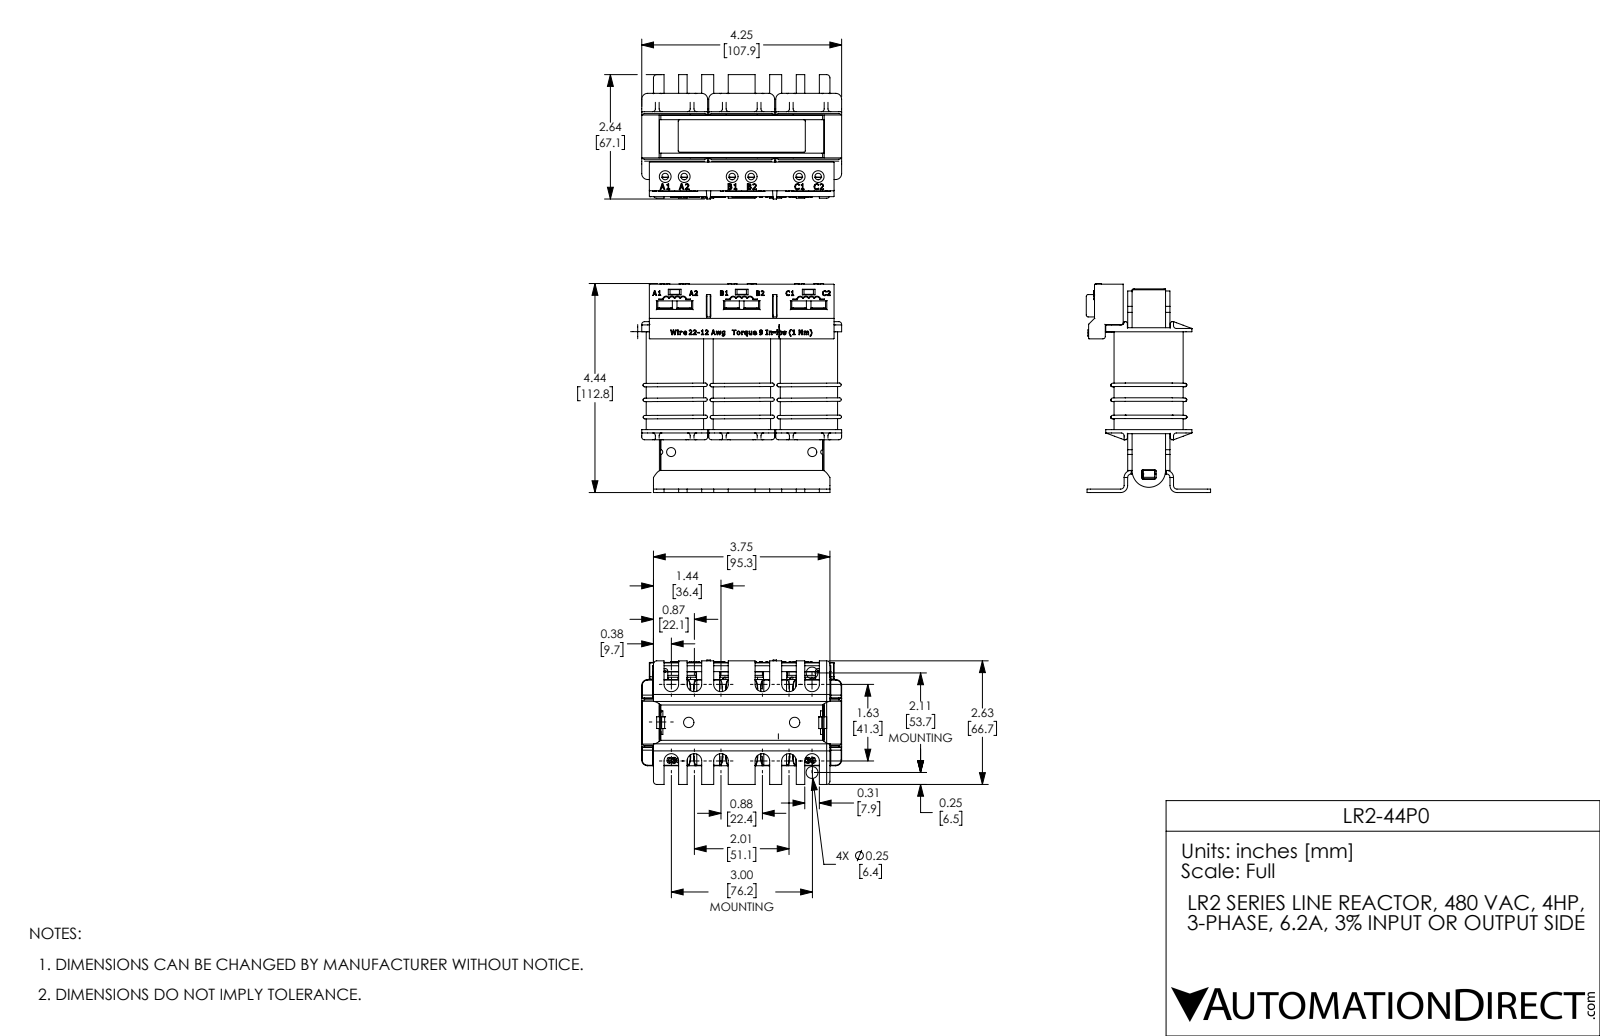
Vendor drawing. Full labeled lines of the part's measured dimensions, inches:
Part name (STEP PRODUCT): AA Frame CoordFix XT from KDR AA Model (107073DG) Rep 2 Ext 2c1 New Mod 2
STEP written by: SolidWorks 2017 (AUTOMOTIVE_DESIGN)
Units: inches
Bodies: 10 solids, 3681 faces (1821 planar, 912 cylindrical, 948 other)
Overall size (bounding box): 4.44 × 4.248 × 2.642
Volume: 19.31 in³ · Surface area: 159.8 in²
Round holes (diameter × count): ⌀0.048 ×6, ⌀0.138 ×6, ⌀0.25 ×6, ⌀0.191 ×4, ⌀0.22 ×2
Round bosses / shafts (diameter × count): ⌀0.175 ×6, ⌀0.068 ×3
Partial cylindrical surfaces — rounded edges, fillets, slot ends (radius × count): R0.01 ×241, R0.035 ×72, R0.06 ×64, R0.03 ×20, R0.24 ×16, R0.059 ×12, R0.075 ×12, R0.125 ×12
Main face-to-face distances: 0.075, 0.07, 1.424, 0.781, 0.898, 0.395, 0.281, 1.179, 1.469, 1.189
Hole centre spacings: 1.424, 0.404, 1.424, 0.469, 1.02, 1.443, 0.236, 0.237
